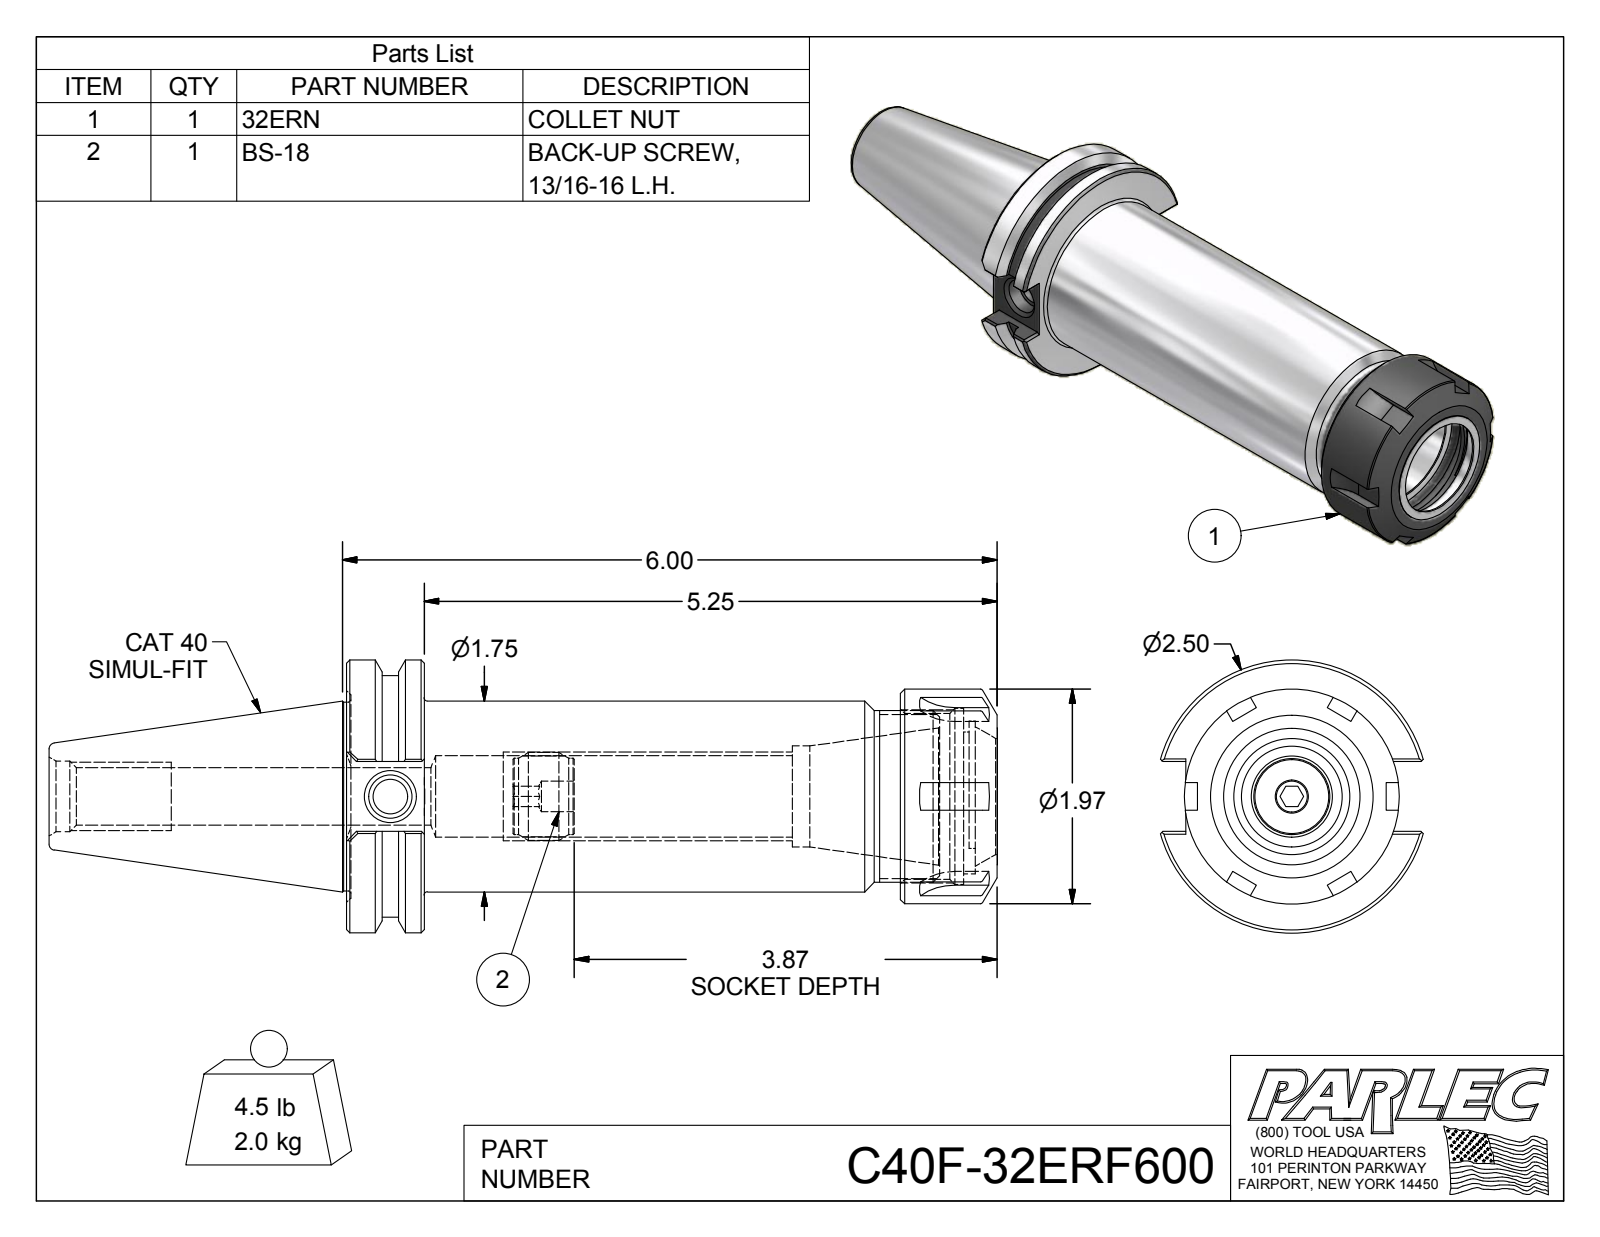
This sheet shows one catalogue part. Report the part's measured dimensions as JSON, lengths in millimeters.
{"part_name": "C40F-32ER6-1; 32ERN; BS-18; C40F-32ERF600", "step_written_by": "Autodesk Inventor 2016 (AUTOMOTIVE_DESIGN)", "units": "millimeters", "bodies": {"solids": 3, "faces": 175, "planar": 75, "cylindrical": 37, "other": 63}, "overall_size": [220.66, 63.5, 61.11], "volume_mm3": 262378, "surface_area_mm2": 54818, "round_holes": [[7.11, 1], [8, 1], [10.13, 1], [13.39, 1], [16.46, 1], [18.92, 1], [23.5, 1], [27, 1], [33.02, 1], [38.65, 1], [41, 1]], "round_bosses_or_shafts": [[63.5, 1], [56.26, 1], [50, 1], [44.45, 1], [40, 1], [20.45, 1], [17.78, 1]], "partial_cylinders_radius": [[0.51, 12], [14.9, 1], [17.5, 1]], "face_to_face_distances": [18.04, 151.39, 133.35, 128.62, 110.58, 22.77, 143.62, 125.58, 15, 7.77], "hole_center_spacings": [1.86]}
